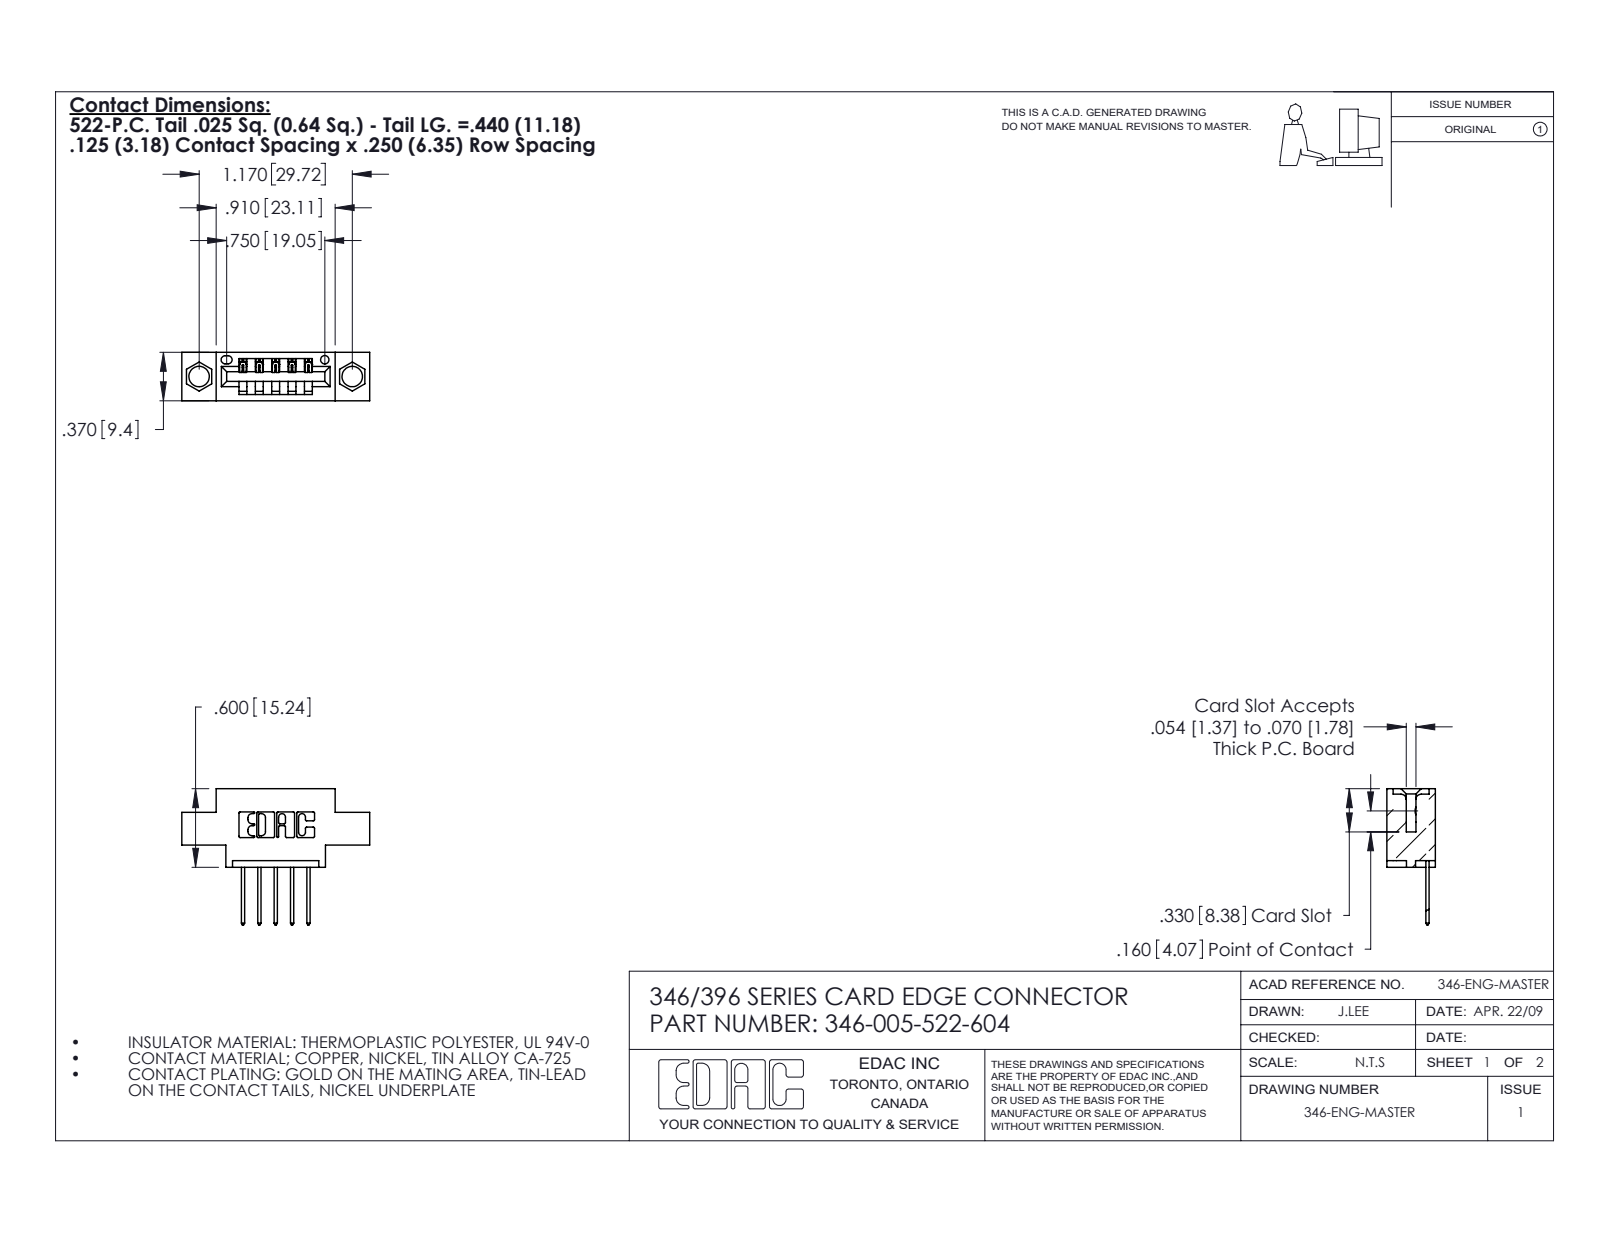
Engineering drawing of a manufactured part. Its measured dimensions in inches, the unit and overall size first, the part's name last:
Units: inches
Overall size (bounding box): 1.435 × 1.04 × 0.37
Round holes (diameter × count): ⌀0.156 ×2, ⌀0.064 ×1
Partial cylindrical surfaces — rounded edges, fillets, slot ends (radius × count): R0.01 ×22, R0.006 ×10, R0.01 ×10, R0.007 ×6, R0.031 ×6, R0.026 ×3, R0.031 ×2, R0.04 ×2
Main face-to-face distances: 0.25, 0.37, 0.048, 0.322, 0.222, 0.148, 0.1, 0.174, 0.55, 0.072
Hole centre spacings: 0.246, 0.969, 1.17
Volume: 0.181 in³ · Surface area: 5.168 in²
Bodies: 6 solids, 430 faces (294 planar, 136 cylindrical, 0 other)
Part name (STEP PRODUCT): 346-005-522-604; 346 Part_0.170 Offset - 0.156 Dia-TH; 345-292-001_345-293-122
STEP written by: SolidWorks 2020 (CONFIG_CONTROL_DESIGN)
